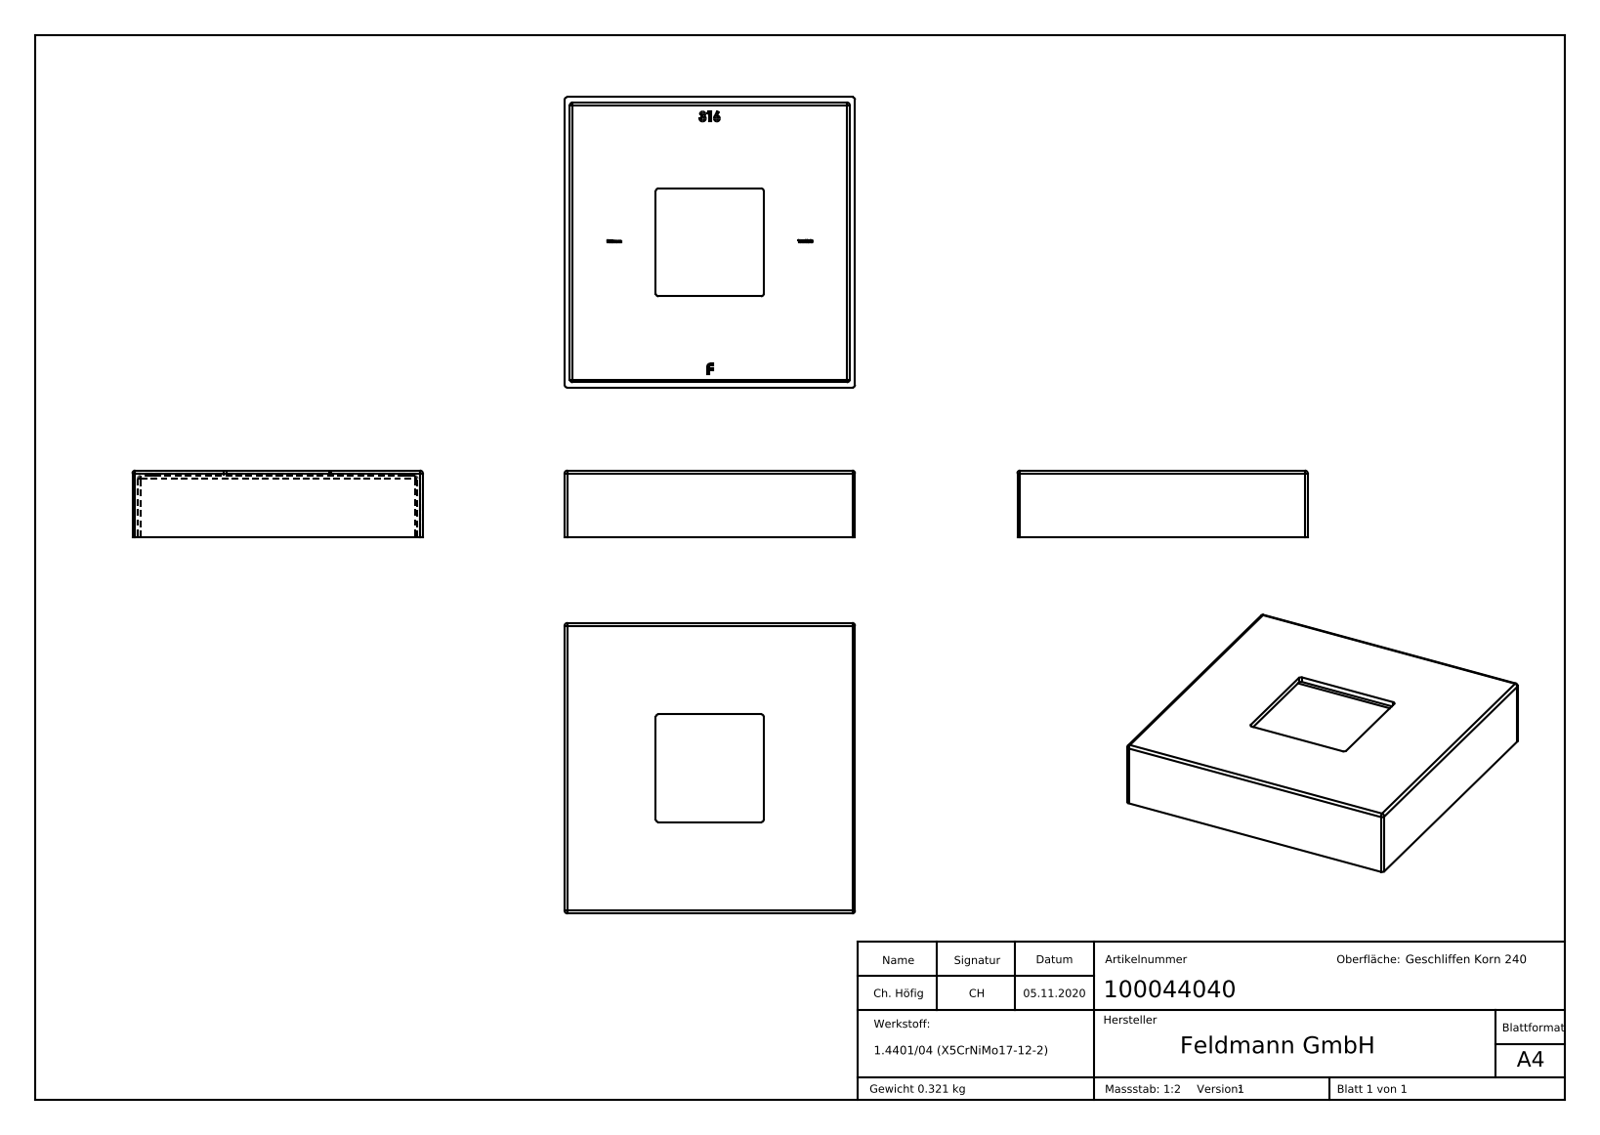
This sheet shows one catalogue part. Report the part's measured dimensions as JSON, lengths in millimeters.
{"part_name": "100044040", "step_written_by": "SolidWorks 2018 (CONFIG_CONTROL_DESIGN)", "units": "millimeters", "bodies": {"solids": 1, "faces": 313, "planar": 169, "cylindrical": 20, "other": 124}, "overall_size": [109, 109, 25], "volume_mm3": 40164, "surface_area_mm2": 40924, "partial_cylinders_radius": [[1, 20]], "face_to_face_distances": [2, 107, 109, 105, 23, 25, 34.25, 32.25, 74.75, 72.75]}
